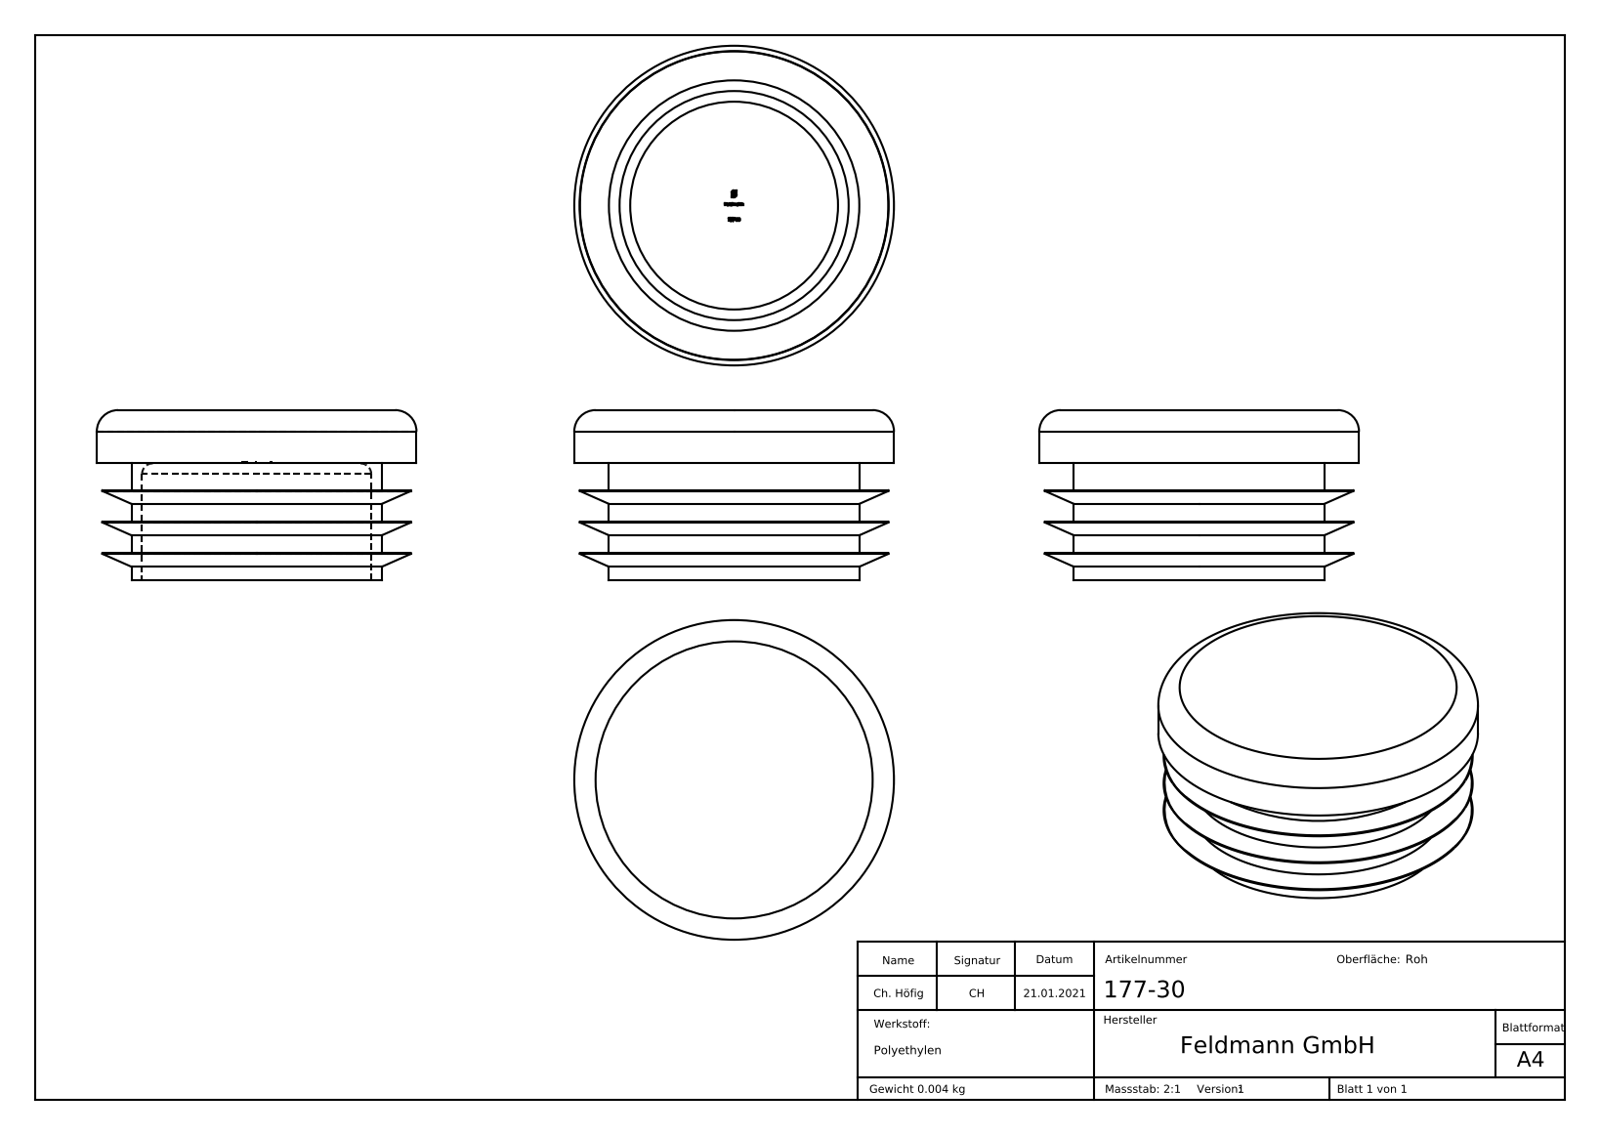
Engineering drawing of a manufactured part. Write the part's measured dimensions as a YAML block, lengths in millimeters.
part_name: "177-30"
step_written_by: "SolidWorks 2018 (CONFIG_CONTROL_DESIGN)"
units: millimeters
bodies: {solids: 1, faces: 230, planar: 125, cylindrical: 6, other: 99}
overall_size: [30, 30, 16]
volume: 4703
surface_area: 4481
round_holes:
  - {diameter: 21.5, count: 1}
round_bosses_or_shafts:
  - {diameter: 30, count: 1}
  - {diameter: 23.5, count: 1}
face_to_face_distances: [5, 2.95, 8.4, 13.4, 5.9, 5.45, 10.45, 2.5, 7.5, 2.6]
